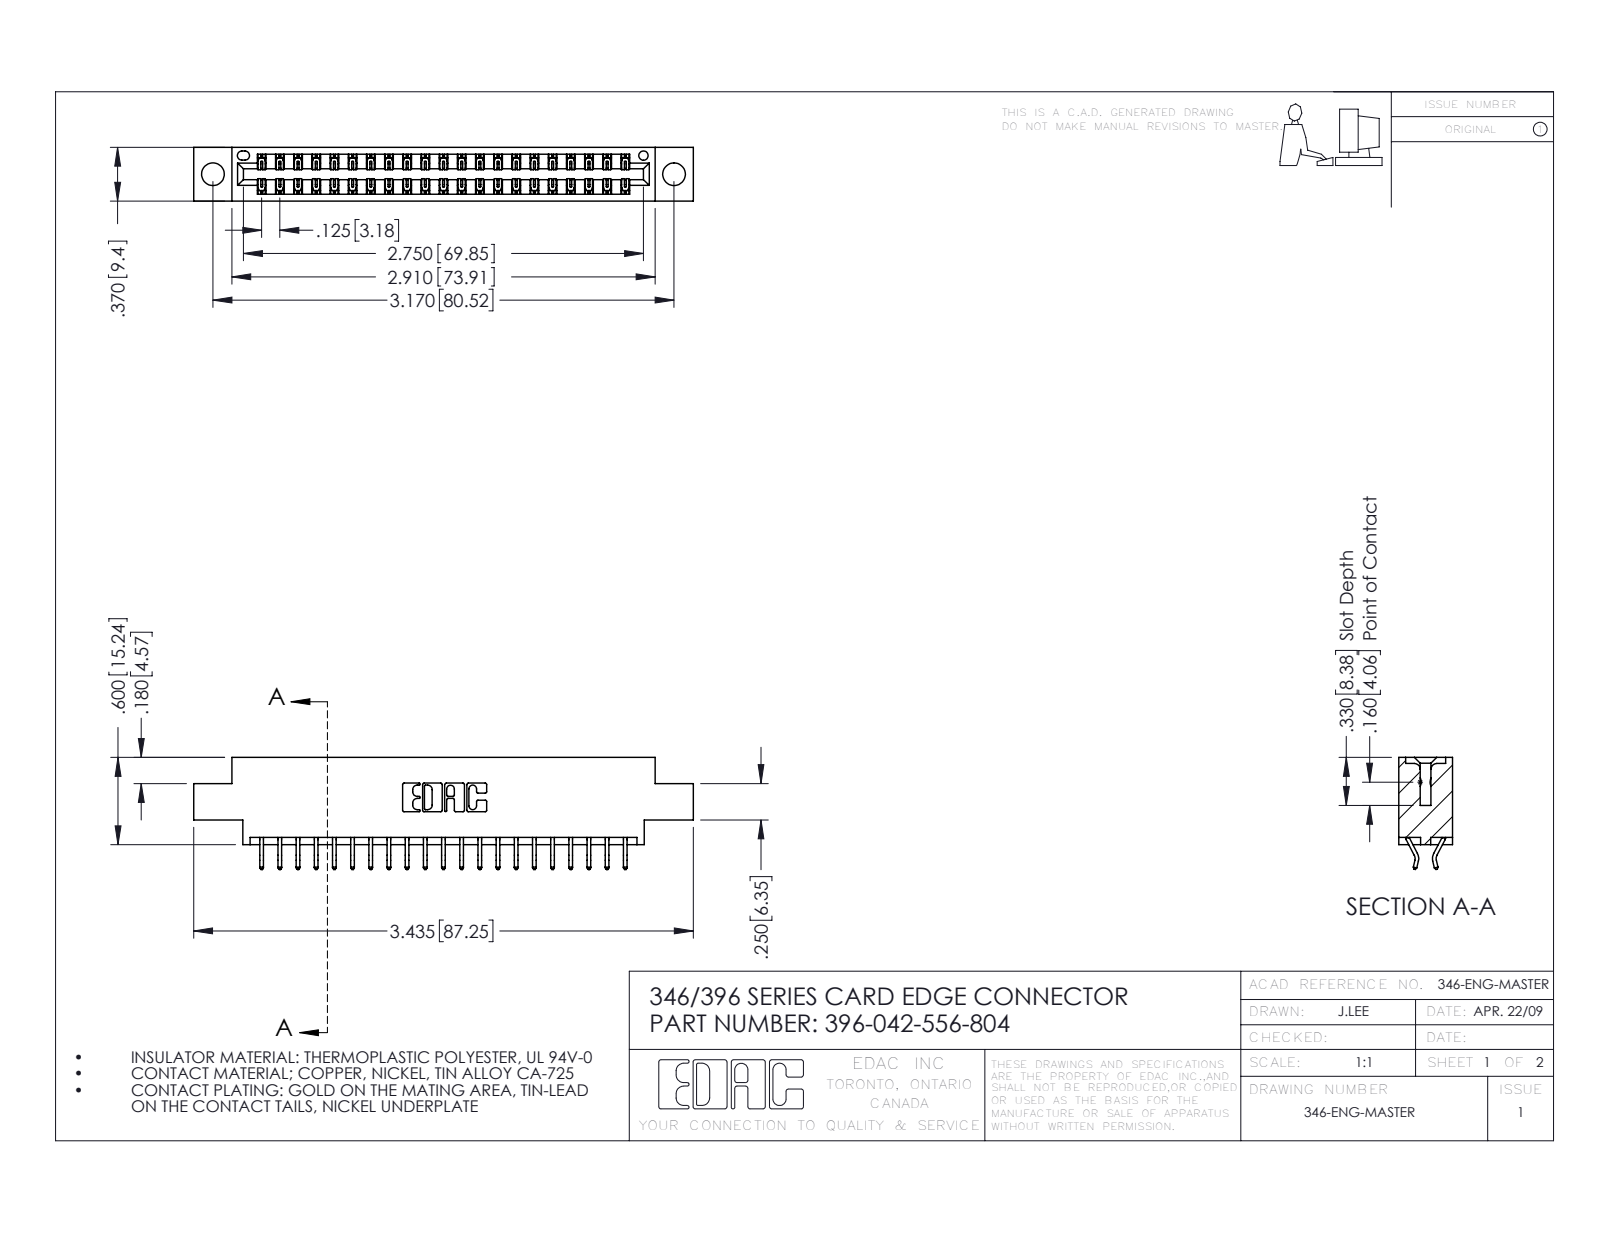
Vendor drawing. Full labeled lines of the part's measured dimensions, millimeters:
Part name (STEP PRODUCT): 345-292-001_556 Tail; 346 Part_0.170 Offset - 0.156 Dia-TH; 396-042-556-804
STEP written by: SolidWorks 2016 (CONFIG_CONTROL_DESIGN)
Units: millimetres
Bodies: 43 solids, 2562 faces (1718 planar, 844 cylindrical, 0 other)
Overall size (bounding box): 87.2 × 19.6 × 9.4
Volume: 8 100 mm³ · Surface area: 10 760 mm²
Round holes (diameter × count): ⌀4 ×2, ⌀1.6 ×1
Partial cylindrical surfaces — rounded edges, fillets, slot ends (radius × count): R0.2 ×63, R0.3 ×22, R0.2 ×6, R0.8 ×6, R0.7 ×3, R0.3 ×2, R0.4 ×2, R0.6 ×2
Main face-to-face distances: 1.2, 8.2, 9.4, 6.4, 0.6, 1.8, 7.6, 7, 3.8, 5.6
Hole centre spacings: 6.2, 75.3, 80.5
